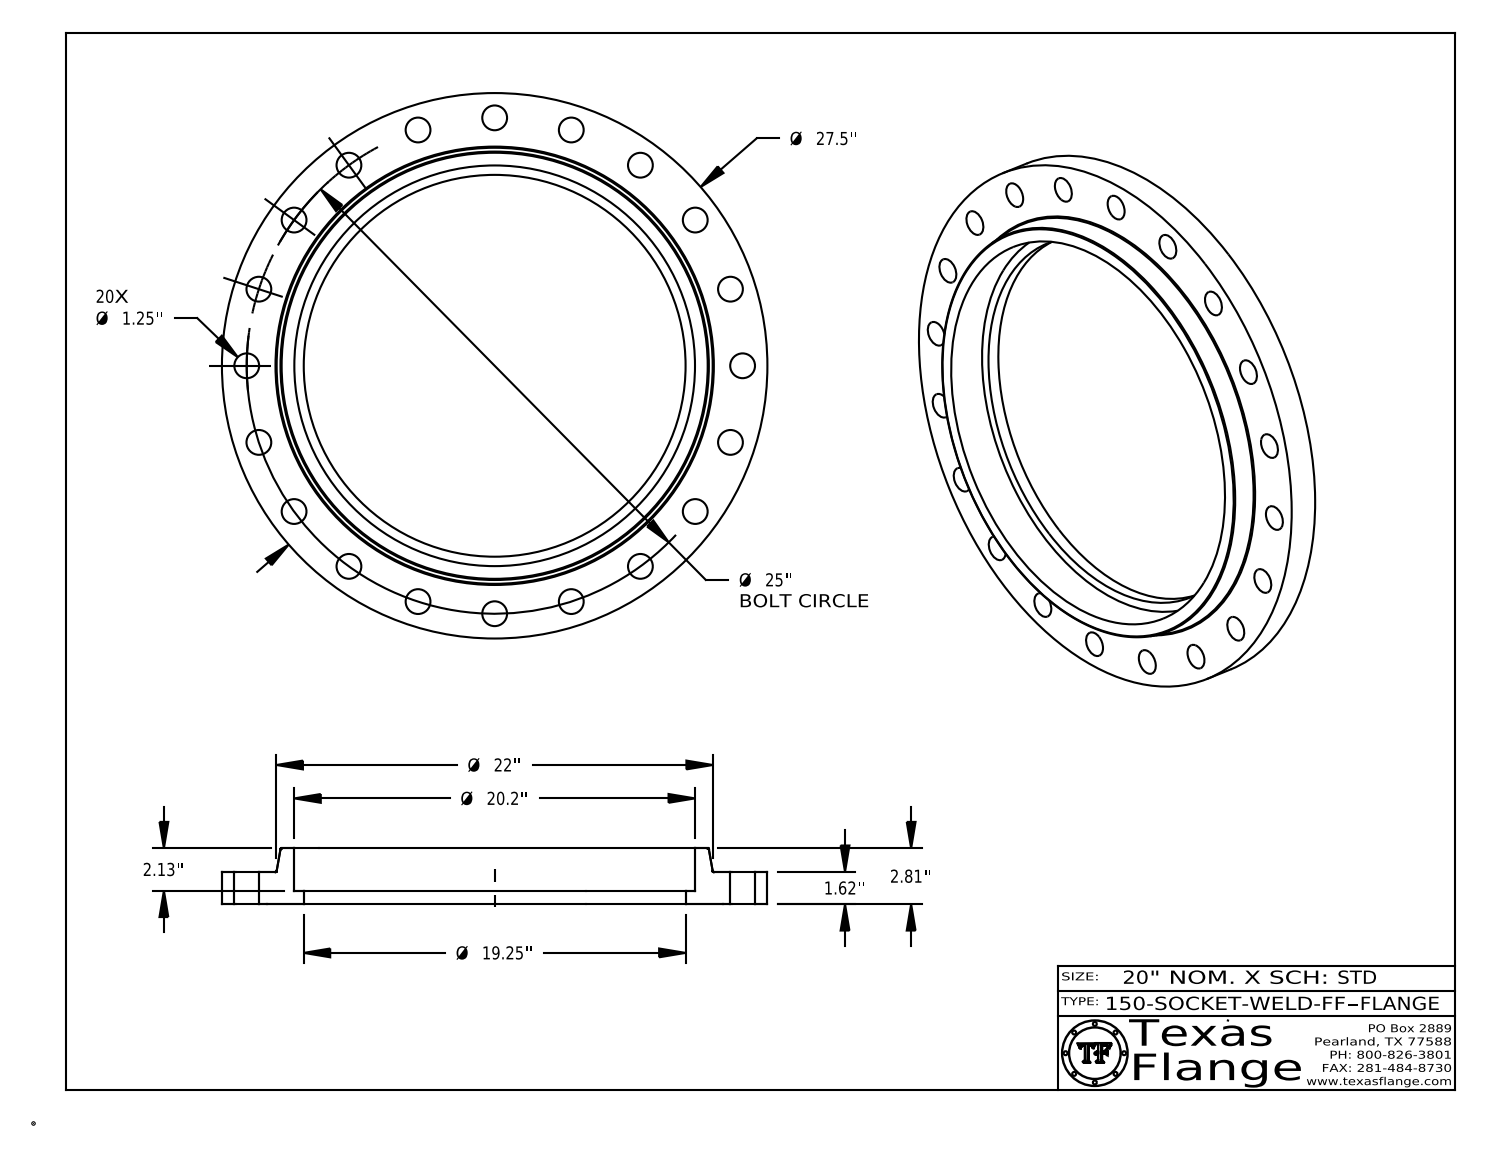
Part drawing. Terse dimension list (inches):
name: 150-SOCKET-WELD-FF
written by: CATIA V5 STEP AP214 (AUTOMOTIVE_DESIGN)
unit: in
bodies: 1 solid, 442 faces (370 planar, 66 cylindrical, 6 other)
size: 27.5 × 27.5 × 2.81
volume: 485.7 in³; area: 1 066 in²
holes: 20× ⌀1.25, 1× ⌀0.495, 1× ⌀19.25, 1× ⌀20.2
bosses: 8× ⌀0.03, 1× ⌀27.5, 1× ⌀0.39
face distances: 1.62, 2.81, 1.19, 0.68, 0.94, 2.13, 1.605, 0.925, 0.015, 1.205
hole spacings: 12.5, 14.694, 17.678, 20.225, 23.776, 24.692, 11.35, 22.275
